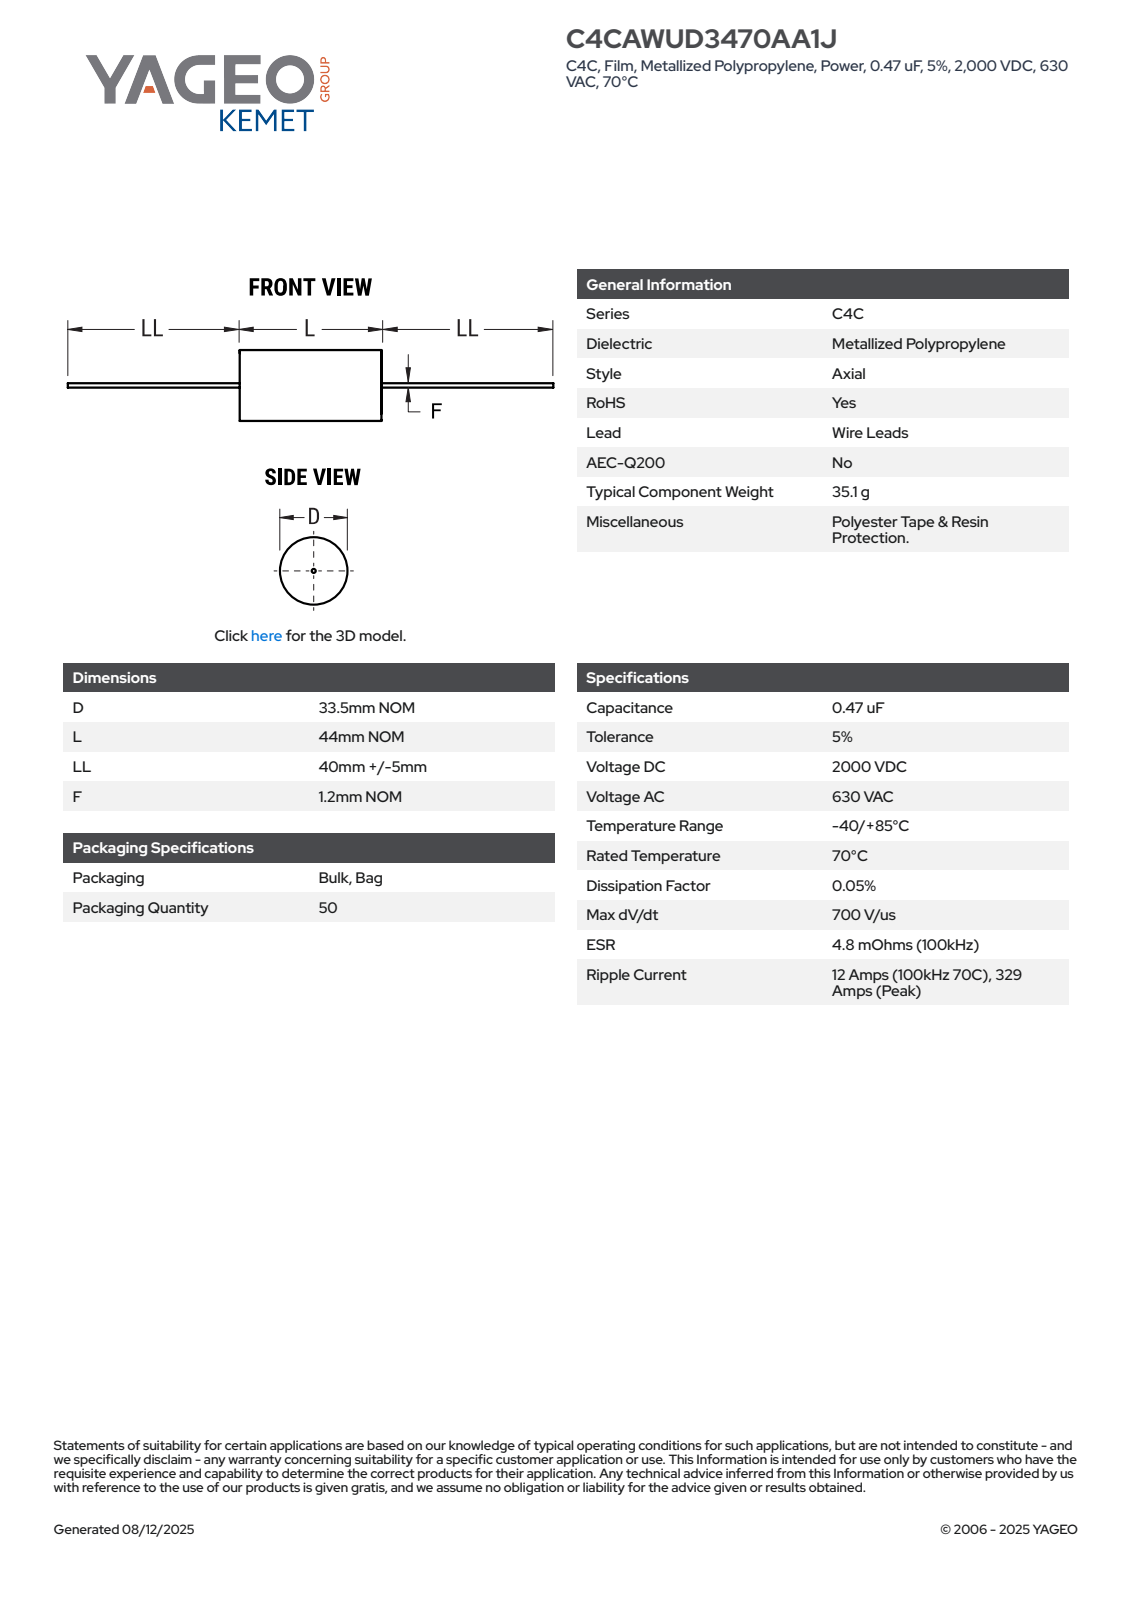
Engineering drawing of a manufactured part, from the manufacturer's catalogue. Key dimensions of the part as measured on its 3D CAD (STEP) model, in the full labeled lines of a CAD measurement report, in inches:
Part name (STEP PRODUCT): CFP_ACWF_33.5X44_D33.5L44LL45F1.2
STEP written by: SolidWorks 2014 (AUTOMOTIVE_DESIGN)
Units: inches
Bodies: 2 solids, 87 faces (28 planar, 28 cylindrical, 31 other)
Overall size (bounding box): 5.276 × 1.319 × 1.319
Volume: 2.373 in³ · Surface area: 13.17 in²
Round bosses / shafts (diameter × count): ⌀1.319 ×1, ⌀0.047 ×1
Partial cylindrical surfaces — rounded edges, fillets, slot ends (radius × count): R0.659 ×1
Main face-to-face distances: 1.732, 1.732, 1.771, 1.772, 3.504, 5.276, 3.504, 3.504, 1.772
